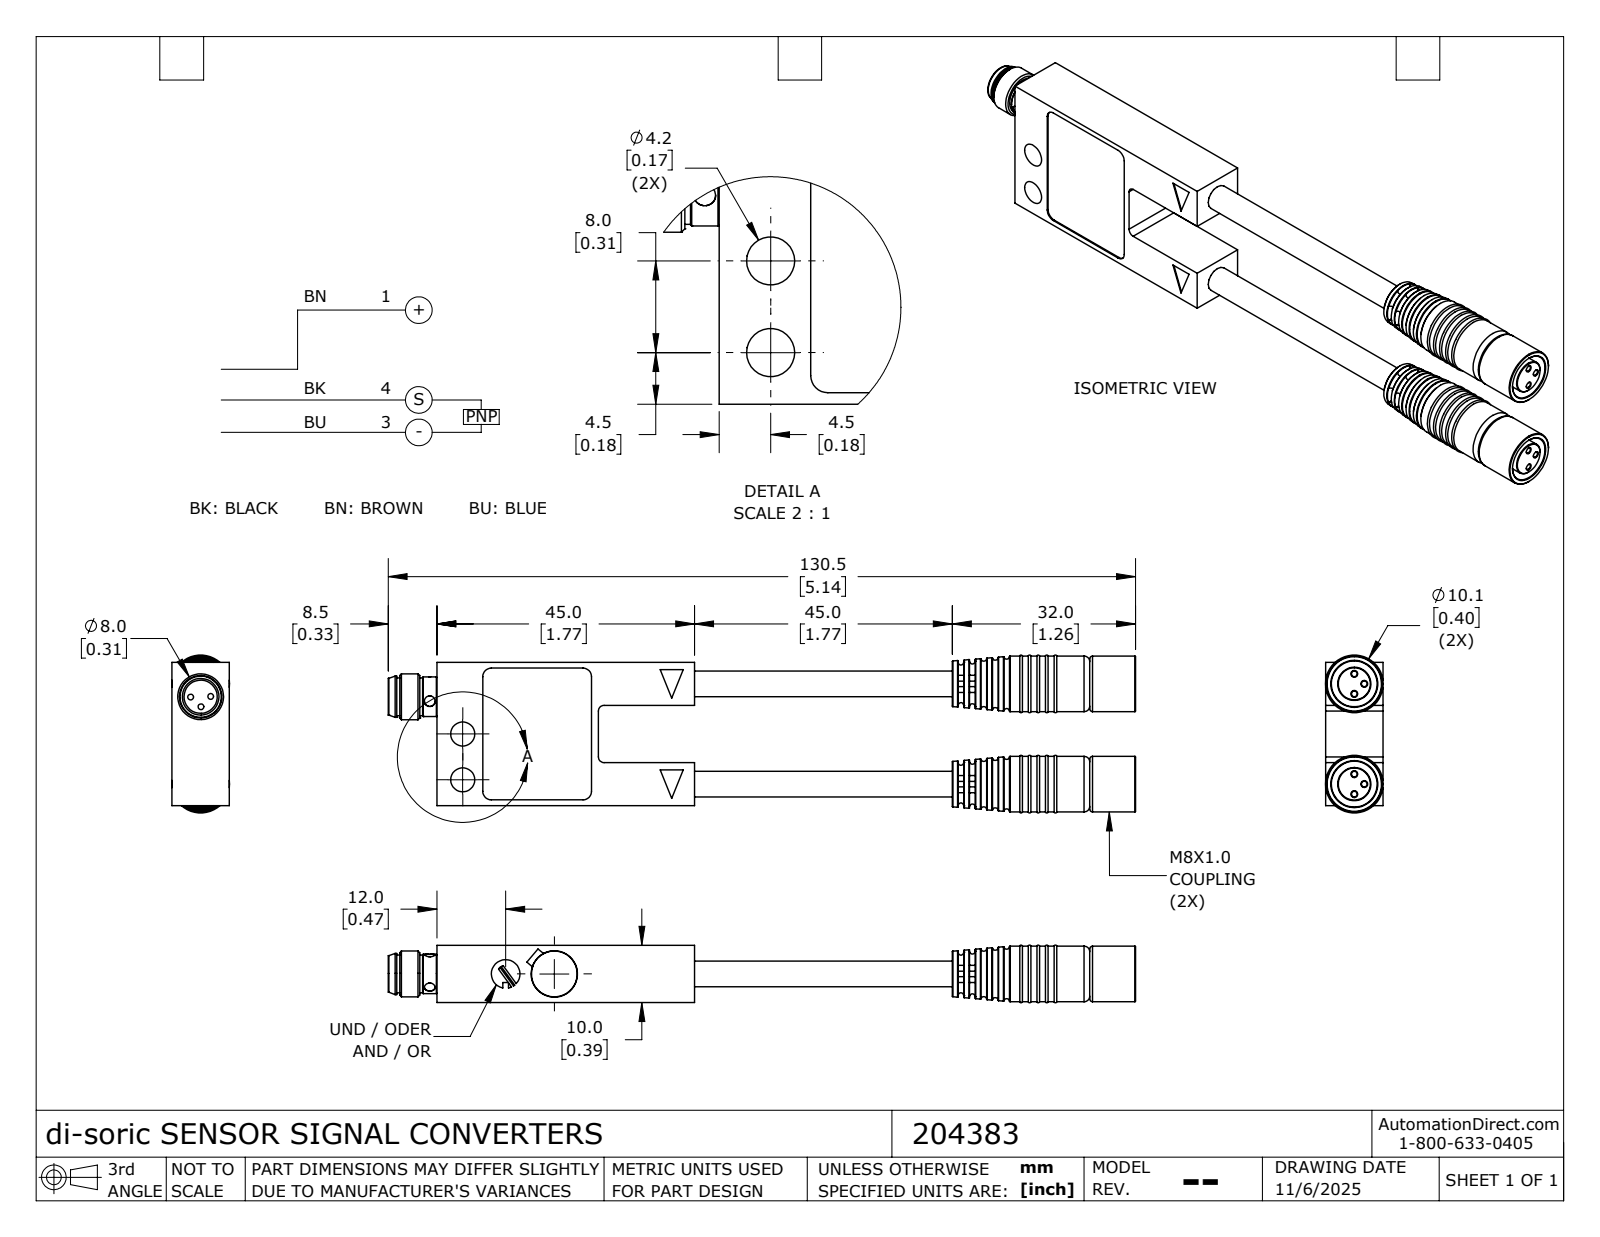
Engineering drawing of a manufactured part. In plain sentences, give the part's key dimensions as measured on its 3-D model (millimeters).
The part is named "AV2-UND_ODER-PS-TS". Its 3-D file was written by "SolidWorks 2024 (AUTOMOTIVE_DESIGN)". It is 1 solid with 318 faces: 164 planar, 66 cylindrical and 88 other. Overall it measures 130.5 by 27.58 by 10.08 millimeters. Its volume is 14 842 cubic millimeters and its surface area 8 934 square millimeters. Round holes: 6 of diameter 1, 3 of diameter 1.9, 2 of diameter 4.2, 2 of diameter 4.6, 2 of diameter 8, 1 of diameter 5, 1 of diameter 5.8, 1 of diameter 8.1. Round bosses or shafts: 3 of diameter 1, 2 of diameter 9.7, 2 of diameter 8, 2 of diameter 5.8, 2 of diameter 4.5, 1 of diameter 7.2, 1 of diameter 7, 1 of diameter 6.9. Partial cylindrical surfaces (rounded edges, fillets, slot ends): 5 of radius 1.5, 2 of radius 0.95, 2 of radius 1. The main face-to-face distances are 10, 25, 9.8, 17.5, 7.5, 1, 45, 2, 3, 24. The hole center spacings are 1.75, 2.47, 17.5, 3.5, 15.75, 15.85, 17.59, 19.25.
